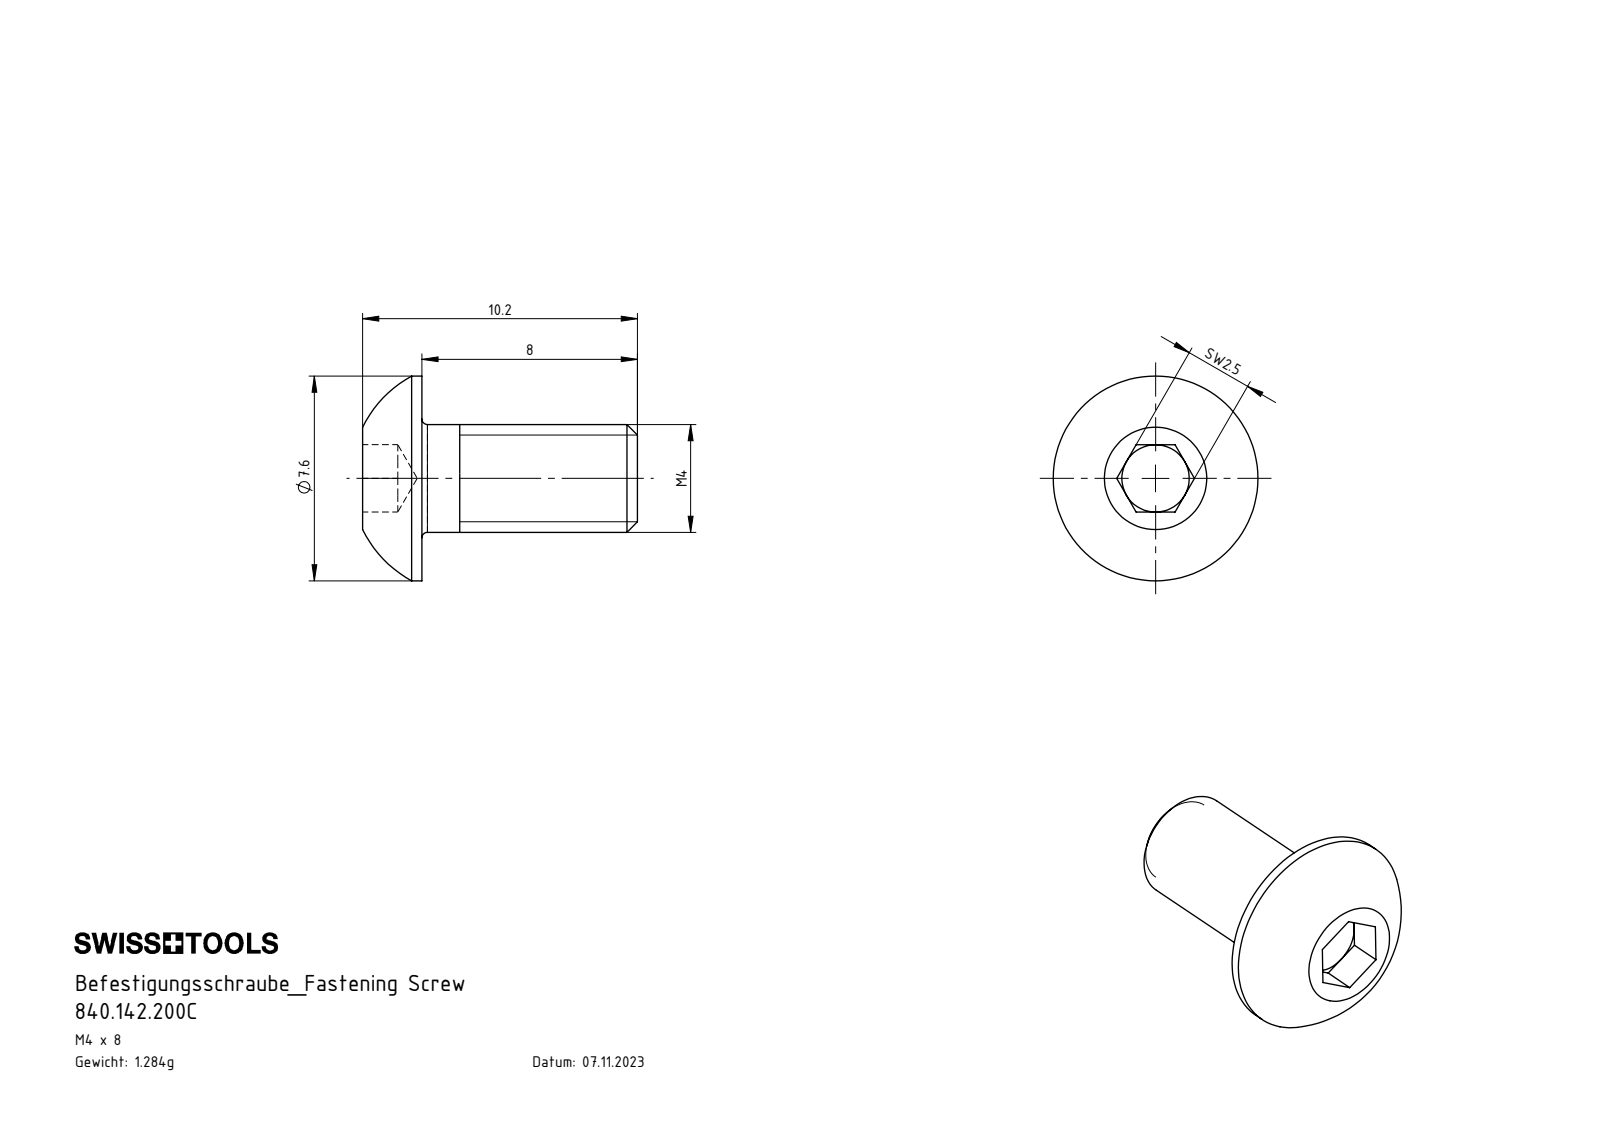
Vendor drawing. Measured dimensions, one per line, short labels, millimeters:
name: 840.142.200C
written by: SolidWorks 2022 (AUTOMOTIVE_DESIGN)
unit: mm
bodies: 1 solid, 27 faces (15 planar, 4 cylindrical, 8 other)
size: 10.2 × 7.6 × 7.6
volume: 164 mm³; area: 224 mm²
bosses: 1× ⌀7.6, 1× ⌀4
face distances: 8, 2.2, 10.2, 2.5, 1.3, 0.9, 8.9
